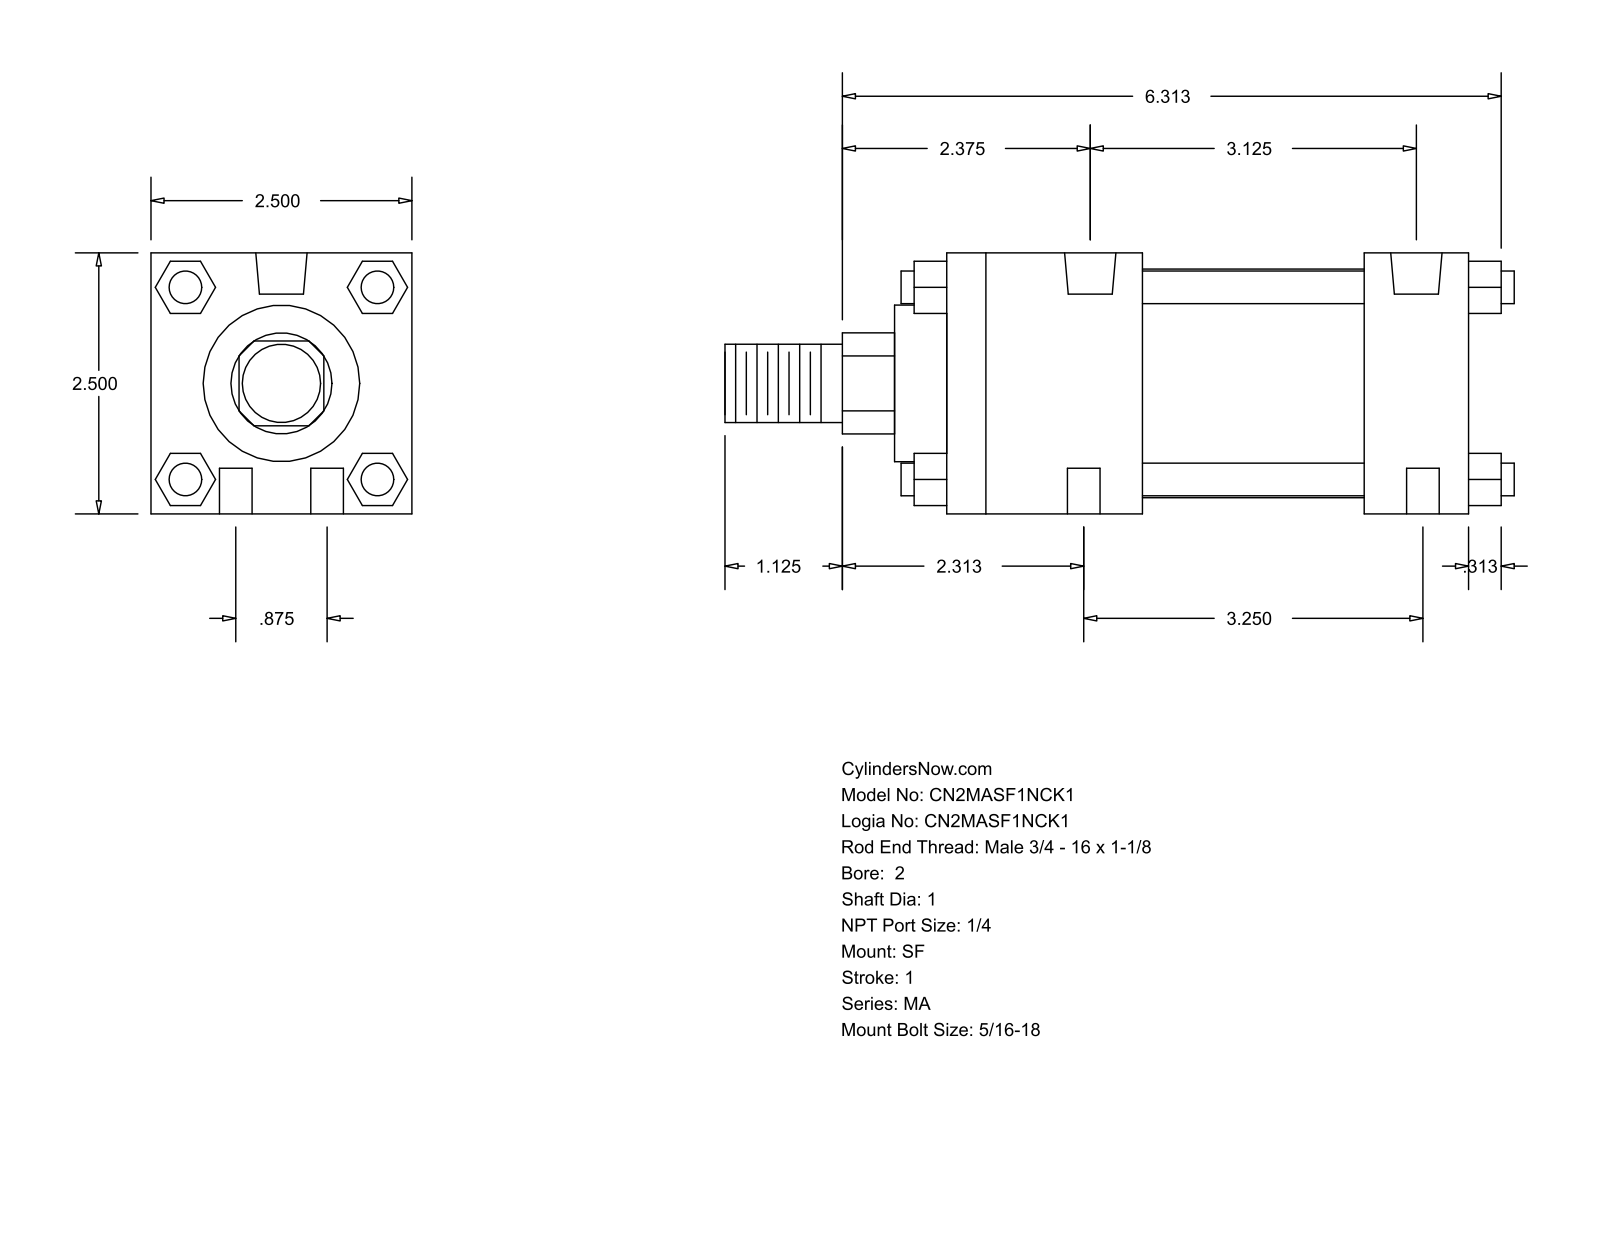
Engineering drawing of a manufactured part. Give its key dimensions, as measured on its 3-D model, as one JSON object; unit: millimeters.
{"part_name": "MA_SF__0200_1", "step_written_by": "GSSL Pune (CONFIG_CONTROL_DESIGN)", "units": "millimeters", "bodies": {"solids": 0, "faces": 124, "planar": 94, "cylindrical": 30, "other": 0}, "overall_size": [192.09, 63.5, 63.5], "round_holes": [[7.94, 6], [12.49, 2]], "round_bosses_or_shafts": [[7.94, 4], [55.63, 1], [38.1, 1], [25.4, 1], [19.05, 1]], "partial_cylinders_radius": [[12.29, 1]], "face_to_face_distances": [63.5, 127, 12.7, 101.6, 53.97, 25.4, 47.63, 79.37, 23.37, 40.47], "hole_center_spacings": [11.22, 81.72, 22.22, 79.37, 82.55, 85.49]}
